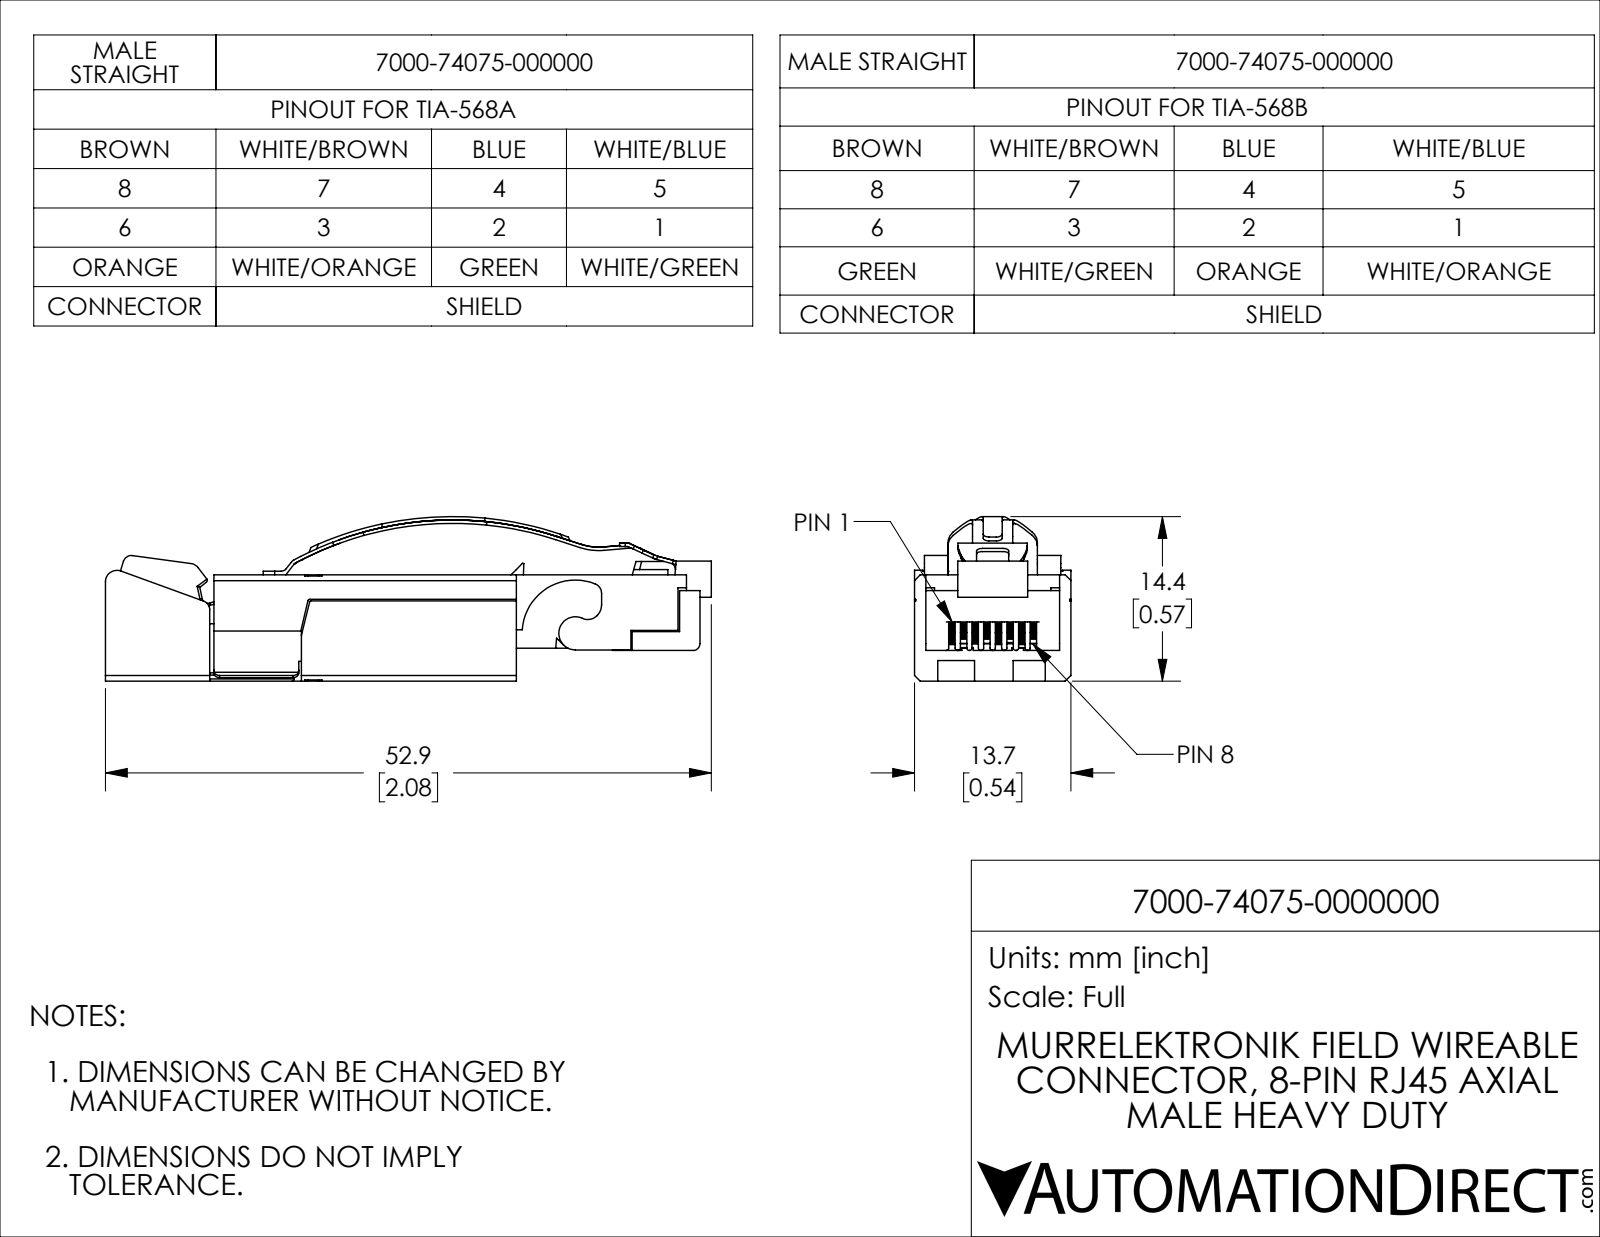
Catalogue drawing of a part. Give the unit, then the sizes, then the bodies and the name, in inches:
Units: inches
Overall size (bounding box): 2.083 × 0.566 × 0.537
Partial cylindrical surfaces — rounded edges, fillets, slot ends (radius × count): R0.009 ×32, R0.02 ×24, R0.008 ×19, R0.012 ×10, R0.02 ×8, R0.039 ×6, R0.197 ×4, R0.016 ×2
Main face-to-face distances: 0.365, 0.537, 0.029, 0.464, 0.509, 0.337, 0.014, 0.323, 0.352, 0.499
Volume: 0.308 in³ · Surface area: 5.892 in²
Bodies: 1 solid, 583 faces (370 planar, 179 cylindrical, 34 other)
Part name (STEP PRODUCT): 7000-74075-0000000
STEP written by: SolidWorks 2021 (CONFIG_CONTROL_DESIGN)
